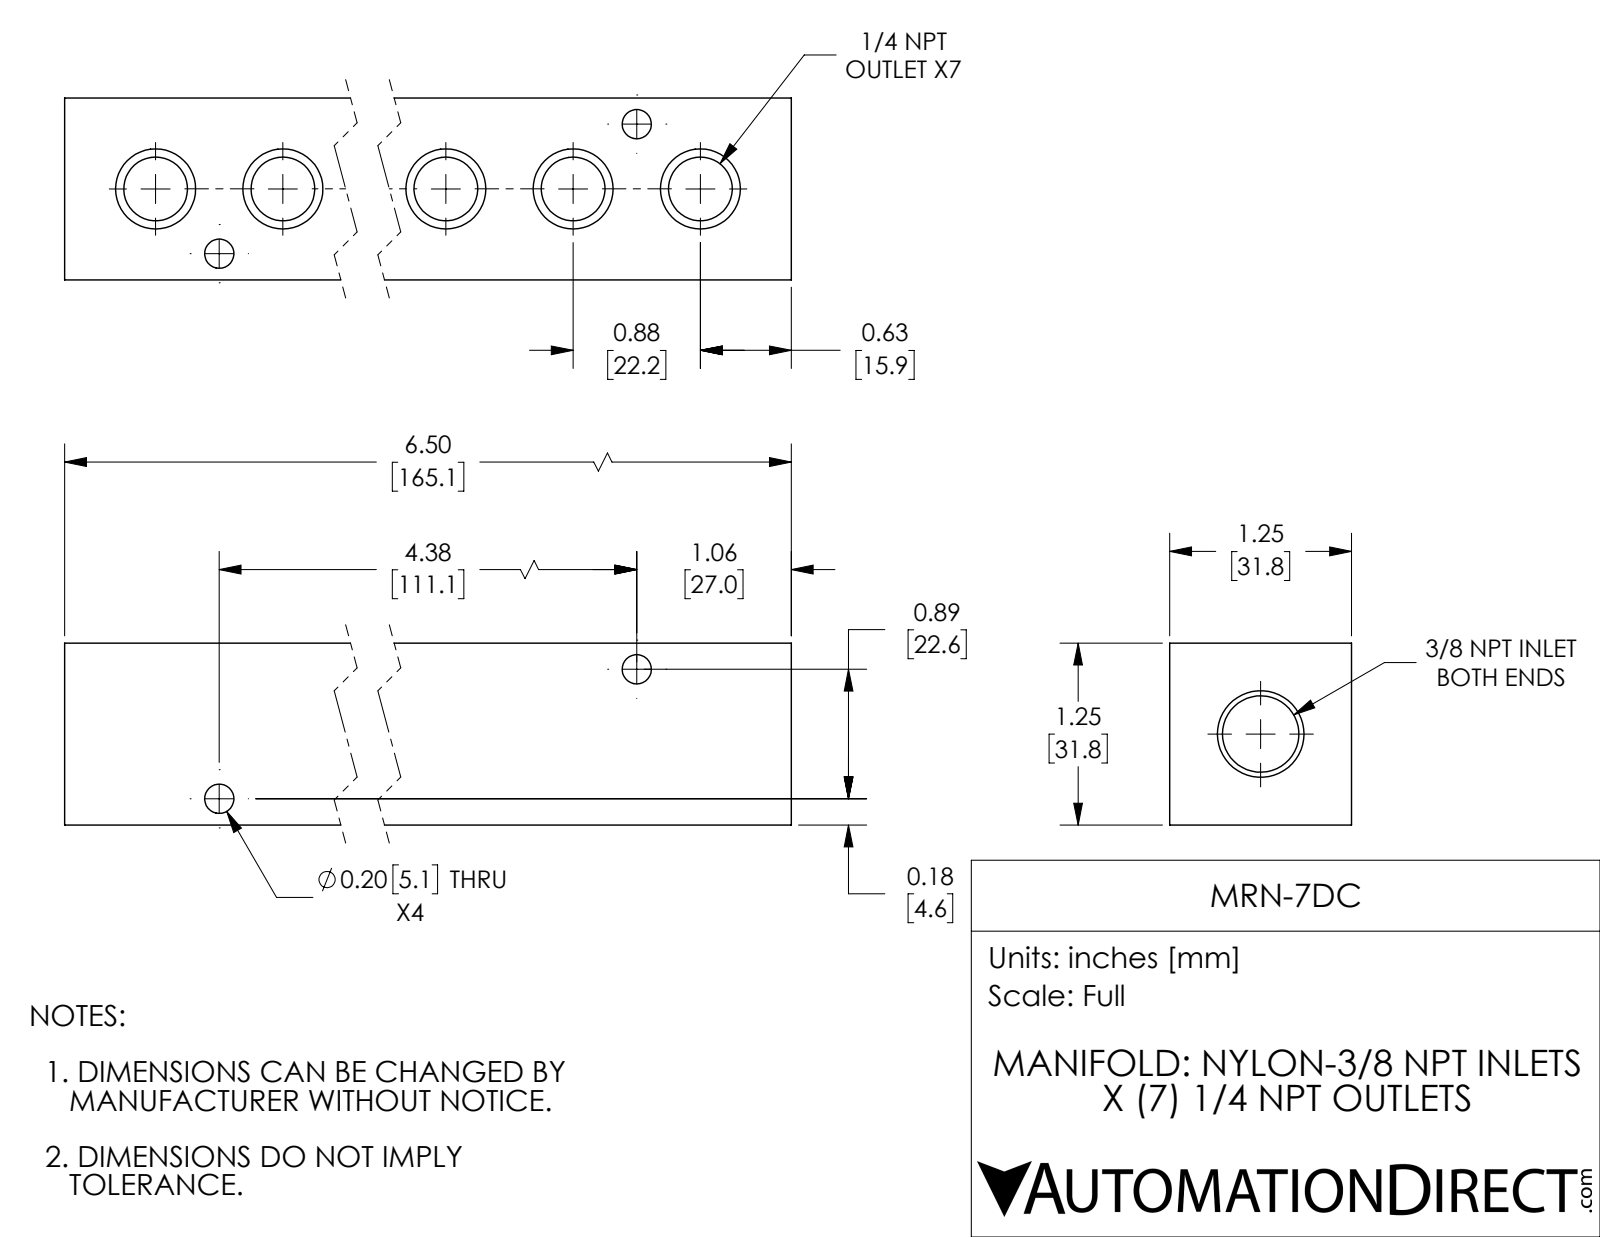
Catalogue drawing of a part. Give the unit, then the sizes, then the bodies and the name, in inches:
Units: inches
Overall size (bounding box): 6.5 × 1.25 × 1.25
Round holes (diameter × count): ⌀0.438 ×7, ⌀0.201 ×4, ⌀0.525 ×1
Main face-to-face distances: 1.25, 6.5
Hole centre spacings: 0.624, 0.875, 1.75, 2.625, 0.875, 2.232, 3.5, 3.963
Volume: 8.174 in³ · Surface area: 49.92 in²
Bodies: 1 solid, 56 faces (6 planar, 32 cylindrical, 18 other)
Part name (STEP PRODUCT): MRN-7DC
STEP written by: SolidWorks 2018 (AUTOMOTIVE_DESIGN)
